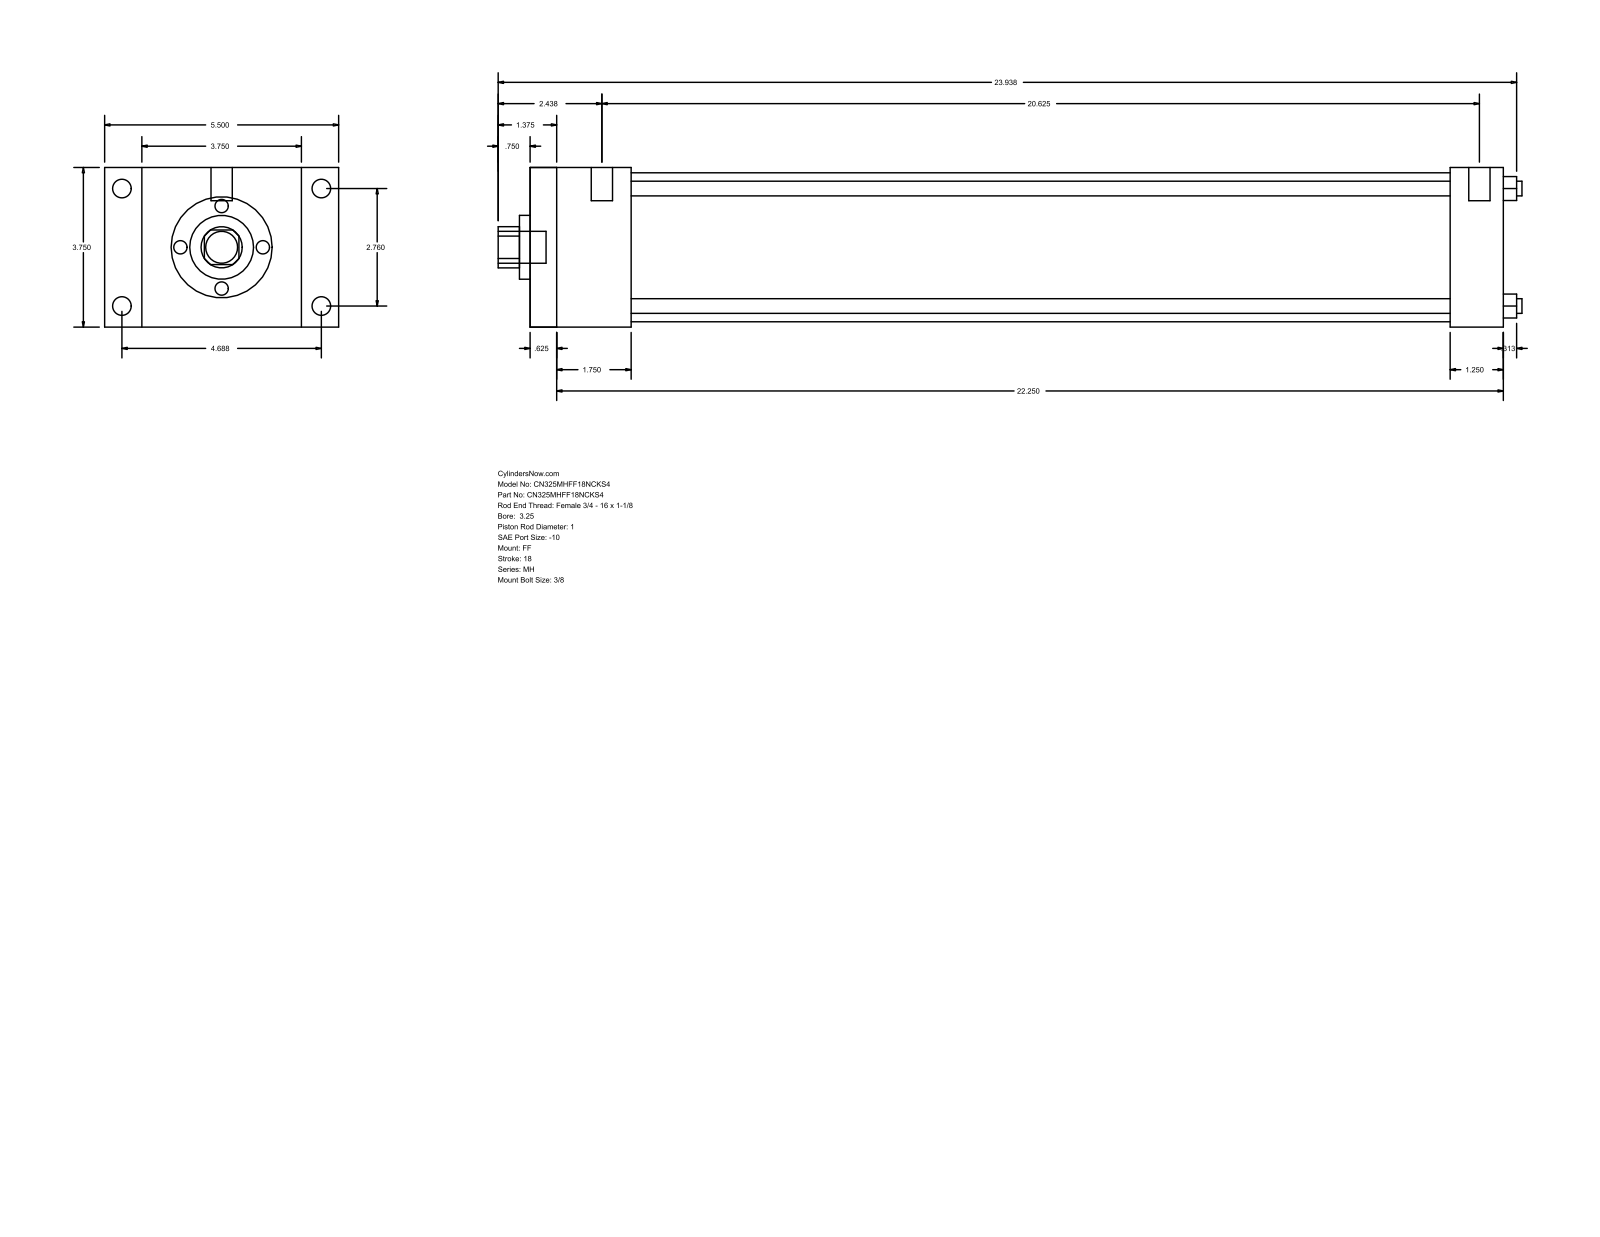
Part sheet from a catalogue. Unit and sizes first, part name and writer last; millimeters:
Units: millimetres
Overall size (bounding box): 611.19 × 139.7 × 95.25
Round holes (diameter × count): ⌀8.76 ×4, ⌀25.4 ×1, ⌀38.1 ×1, ⌀88.9 ×1
Round bosses / shafts (diameter × count): ⌀11.13 ×4, ⌀5.56 ×4, ⌀12.7 ×2, ⌀19.05 ×1
Partial cylindrical surfaces — rounded edges, fillets, slot ends (radius × count): R12.29 ×1
Main face-to-face distances: 95.24, 581.03, 15.87, 565.16, 22.23, 117.47, 549.28, 533.41, 31.75, 60.33
Hole centre spacings: 49.57, 70.1, 99.14
Bodies: 0 solids, 92 faces (64 planar, 28 cylindrical, 0 other)
Part name (STEP PRODUCT): MH_FF__0325_1
STEP written by: GSSL Pune (CONFIG_CONTROL_DESIGN)
